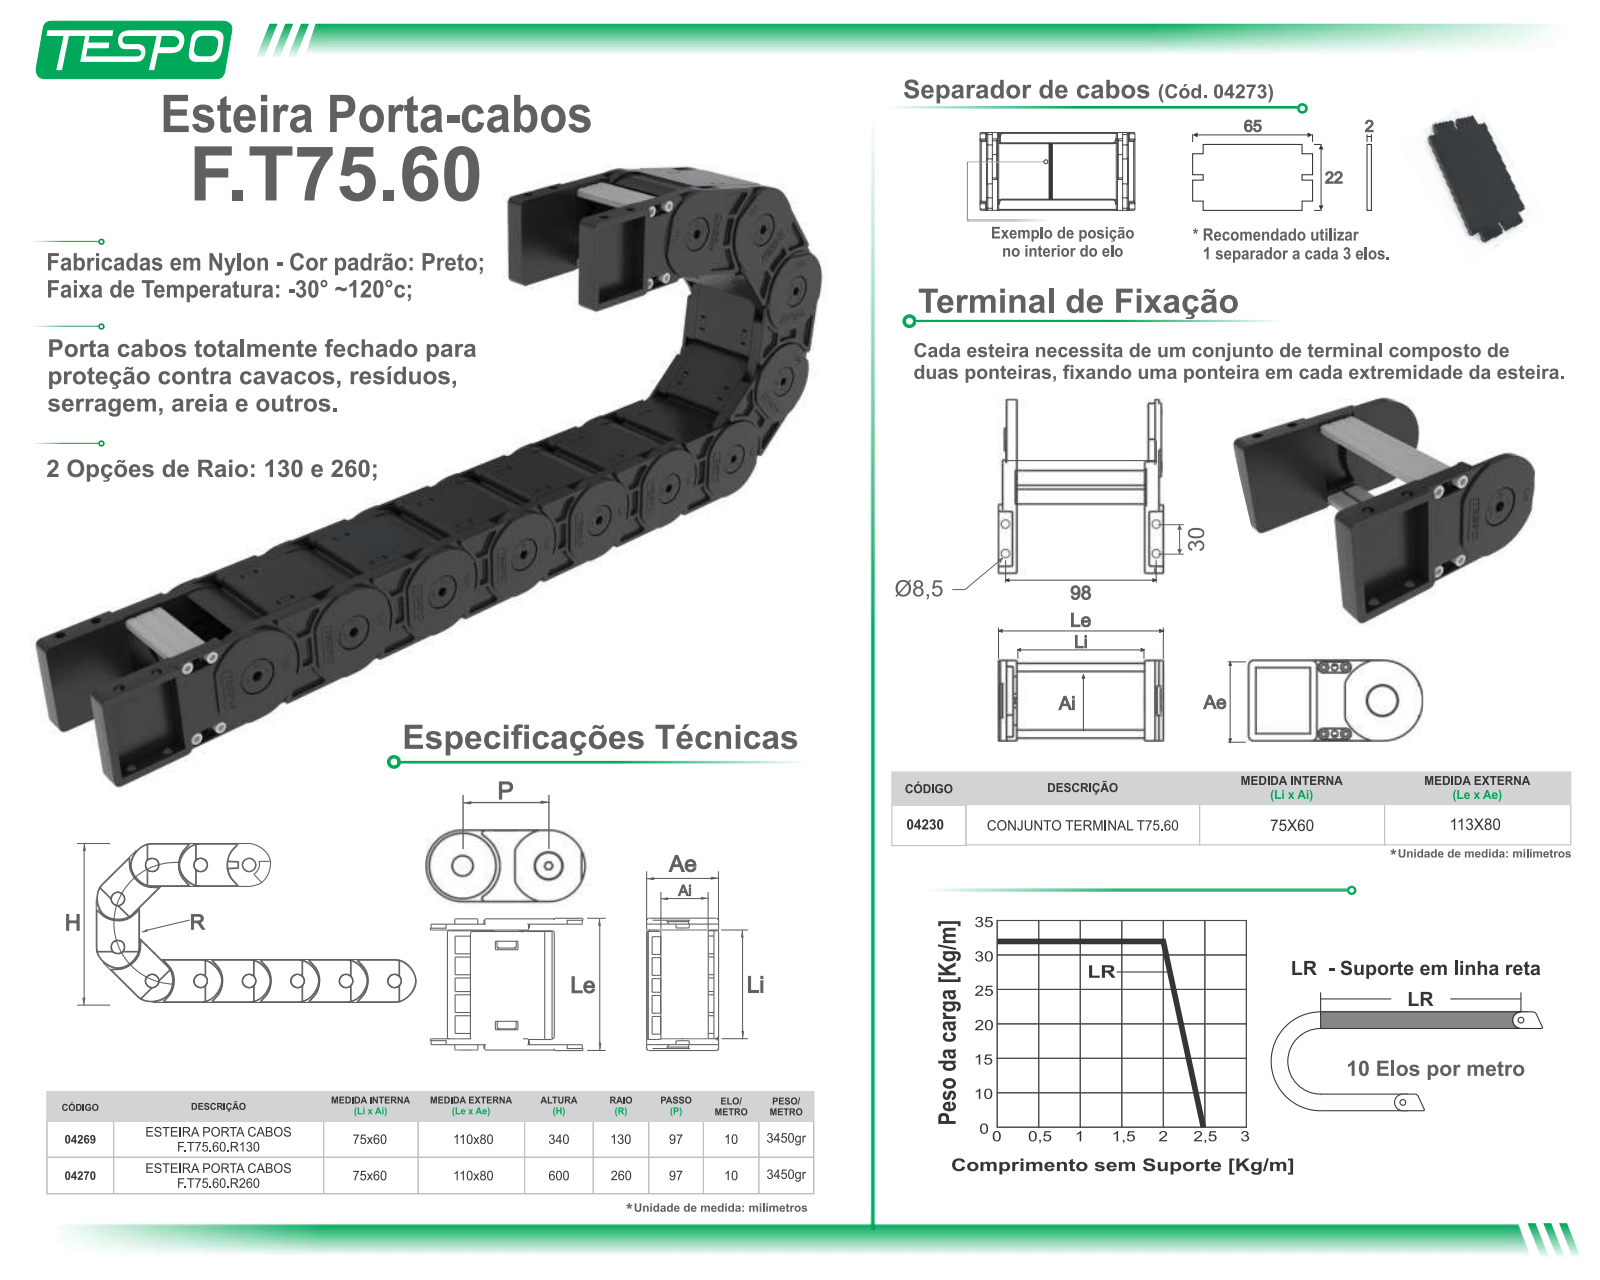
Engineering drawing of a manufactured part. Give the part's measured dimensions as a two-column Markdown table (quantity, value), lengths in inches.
| quantity | value |
| --- | --- |
| STEP written by | ST-DEVELOPER v15 (AUTOMOTIVE_DESIGN) |
| units | inches |
| bodies | 1 solid, 96 faces (57 planar, 0 cylindrical, 39 other) |
| overall size | 7.047 × 4.276 × 3.228 |
| volume | 23.4 in³ |
| surface area | 165 in² |
| main face-to-face distances | 0.433, 0.661, 3.614, 0.524, 3.752, 0.138, 3.091, 0.516, 3.76, 0.146 |
